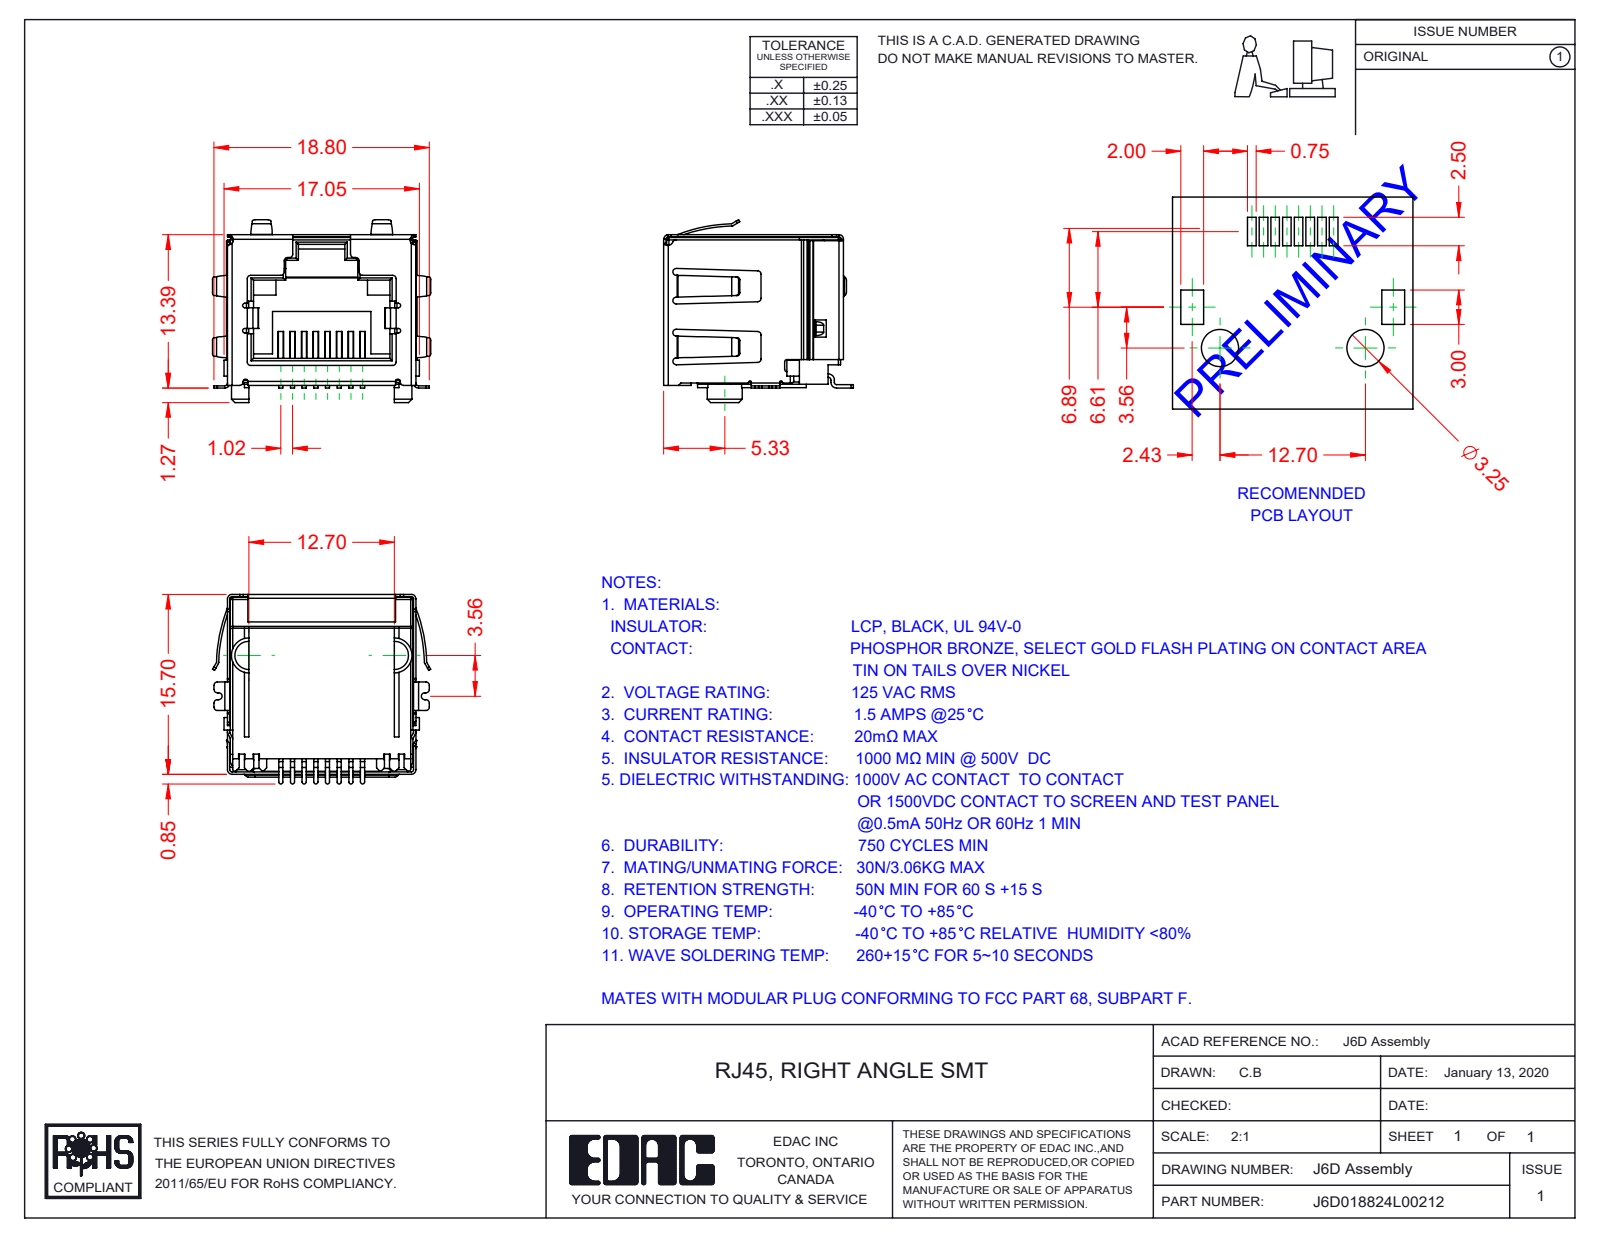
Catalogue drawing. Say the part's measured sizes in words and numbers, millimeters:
The part is named "J6D018824L00212; 6D Insulator; 6D Shield_No LED - EMI; 6D Contacts". Its 3-D file was written by "SolidWorks 2016 (CONFIG_CONTROL_DESIGN)". It is 10 solids with 962 faces: 653 planar, 264 cylindrical and 45 other. Overall it measures 19.06 by 16.55 by 15.95 millimeters. Its volume is 1 678 cubic millimeters and its surface area 4 487 square millimeters. Partial cylindrical surfaces (rounded edges, fillets, slot ends): 55 of radius 0.3, 40 of radius 0.2, 19 of radius 0.4, 16 of radius 0.25, 12 of radius 0.1, 8 of radius 0.15, 8 of radius 0.18, 6 of radius 0.5. The main face-to-face distances are 16, 16.2, 16.25, 2.25, 15.95, 0.45, 13.05, 10.6, 12.85, 12.8.
